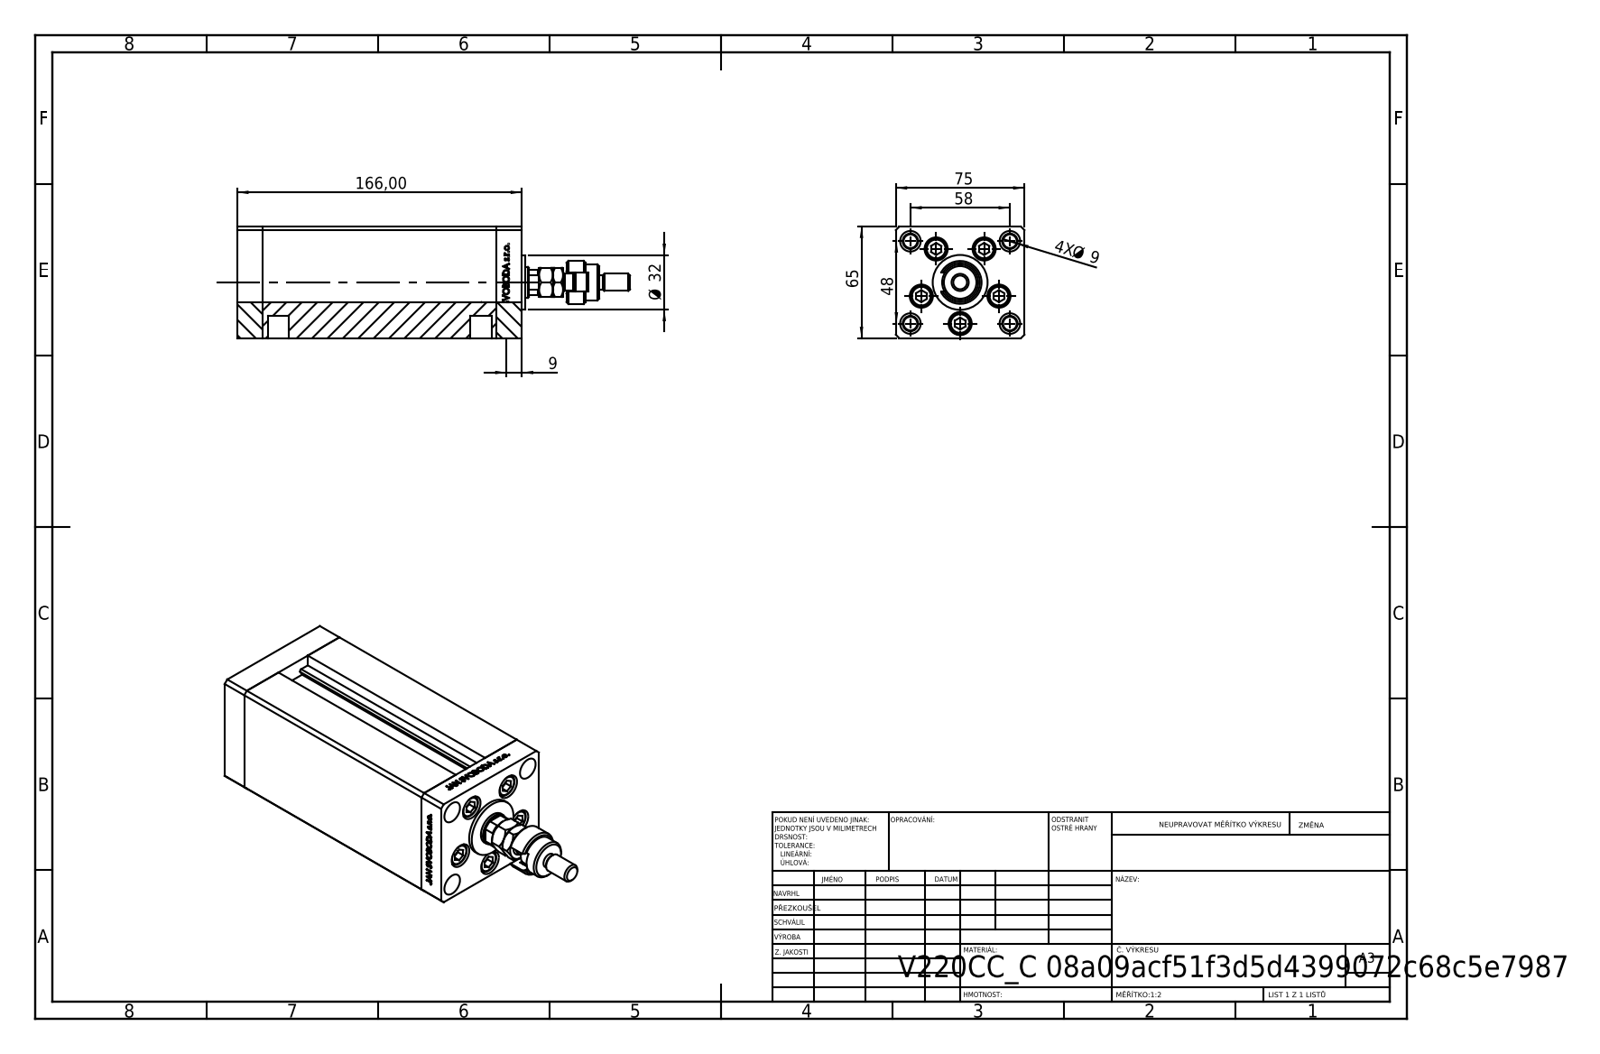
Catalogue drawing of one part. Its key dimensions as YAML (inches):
part_name: "MFA; ALLEN BOLT; V220C_C MIDDLE; V220C FRONT (+3 more)"
step_written_by: "SolidWorks 2019 (CONFIG_CONTROL_DESIGN)"
units: inches
bodies: {solids: 15, faces: 1264, planar: 570, cylindrical: 188, other: 506}
overall_size: [9.016, 2.953, 2.559]
volume: 42.03
surface_area: 231.2
round_holes:
  - {diameter: 0.354, count: 9}
  - {diameter: 0.531, count: 5}
  - {diameter: 0.079, count: 4}
  - {diameter: 0.315, count: 4}
  - {diameter: 0.472, count: 4}
  - {diameter: 0.518, count: 4}
  - {diameter: 0.335, count: 1}
  - {diameter: 0.492, count: 1}
  - {diameter: 0.709, count: 1}
round_bosses_or_shafts:
  - {diameter: 0.315, count: 6}
  - {diameter: 0.492, count: 4}
  - {diameter: 1.26, count: 1}
  - {diameter: 0.984, count: 1}
  - {diameter: 0.827, count: 1}
  - {diameter: 0.63, count: 1}
  - {diameter: 0.394, count: 1}
partial_cylinders:
  - {radius: 0.037, count: 2}
  - {radius: 0.217, count: 1}
  - {radius: 0.335, count: 1}
  - {radius: 0.344, count: 1}
face_to_face_distances: [2.953, 2.559, 5.354, 0.591, 5.945, 6.535, 1.102, 0.512, 2.146, 0.413]
hole_center_spacings: [0.945, 1.482, 0.617, 0.678, 1.091, 1.135, 1.142, 1.285]
